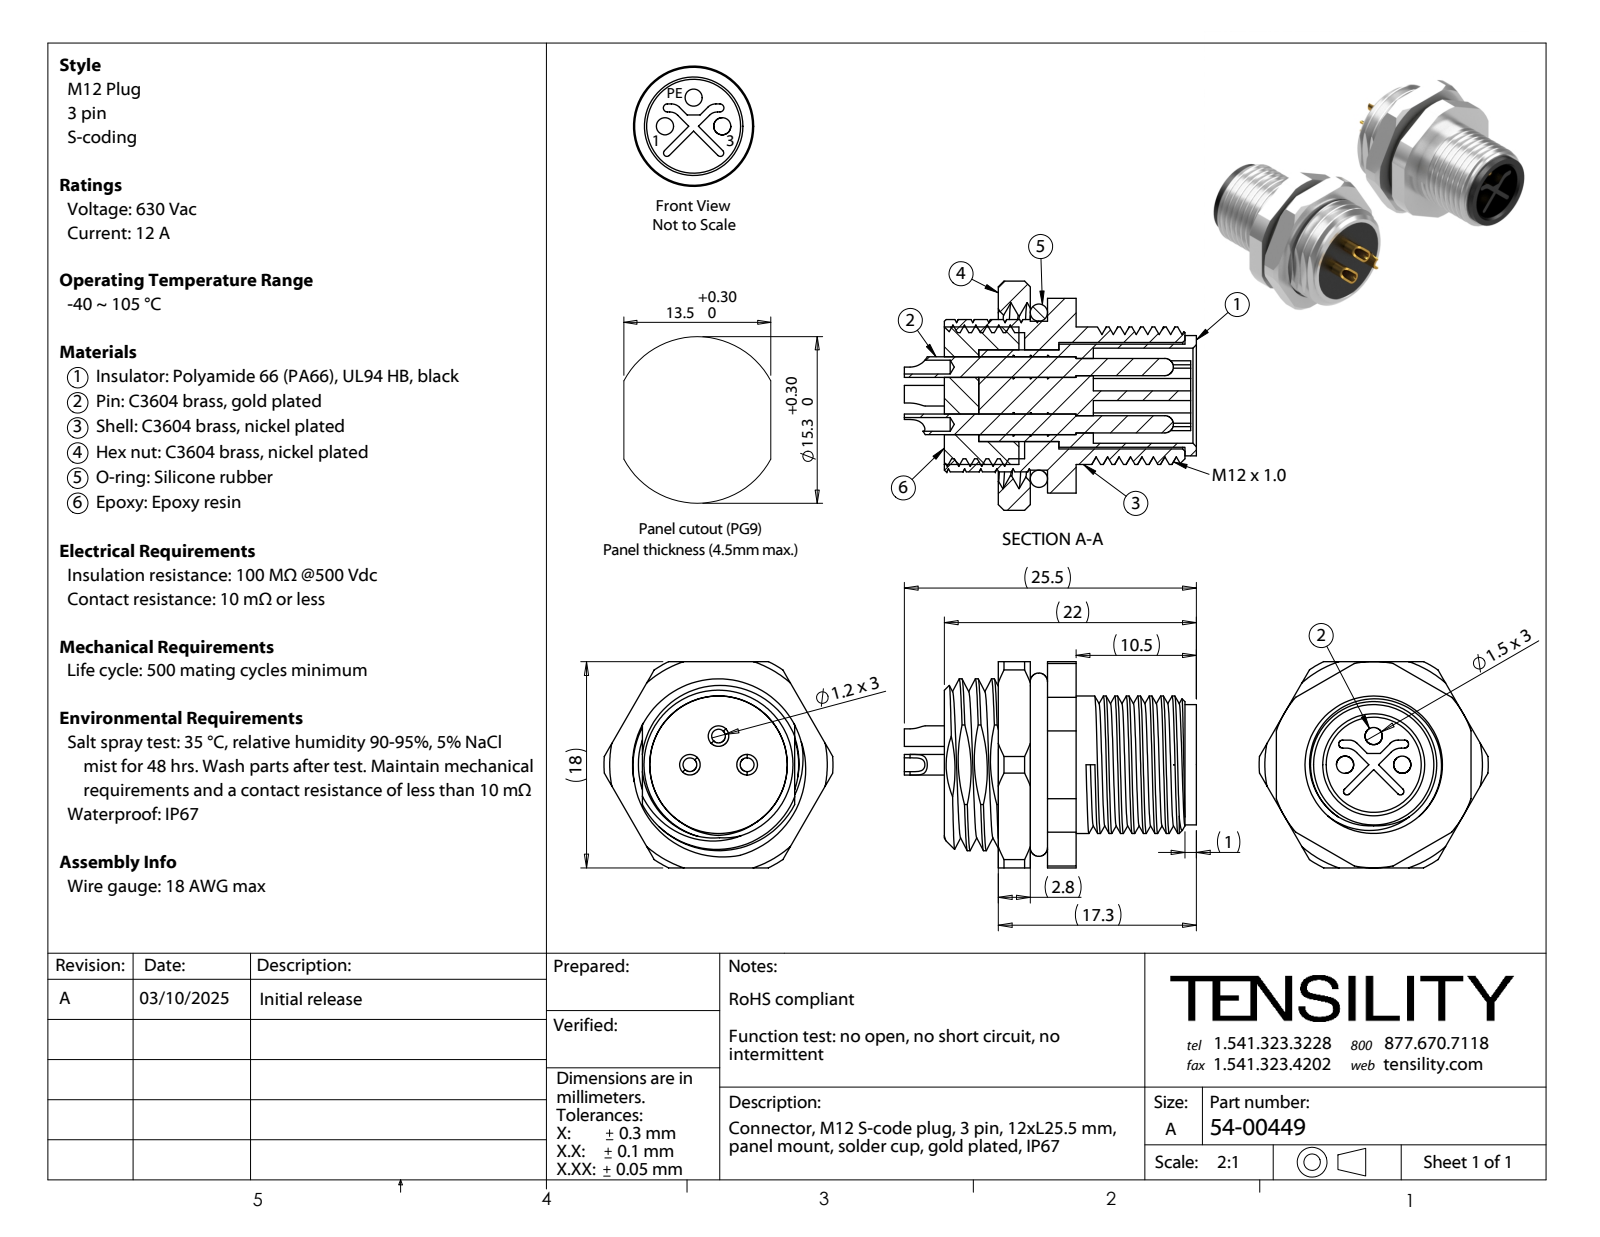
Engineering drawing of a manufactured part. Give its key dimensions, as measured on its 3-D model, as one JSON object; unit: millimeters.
{"part_name": "54-00449-03; 54-00449-02; 54-00449; 54-00449-03L (+3 more)", "step_written_by": "SolidWorks 2021 (CONFIG_CONTROL_DESIGN)", "units": "millimeters", "bodies": {"solids": 8, "faces": 309, "planar": 83, "cylindrical": 144, "other": 82}, "overall_size": [25.5, 20, 18], "volume_mm3": 3000, "surface_area_mm2": 5707, "round_holes": [[1.2, 3], [1.5, 3], [8, 1], [8.3, 1], [9.3, 1], [11, 1], [14, 1]], "round_bosses_or_shafts": [[1.8, 3], [13, 1], [12, 1], [10.5, 1], [9, 1]], "partial_cylinders_radius": [[0.3, 2], [0.35, 2], [1, 2], [1.28, 2], [1.7, 2], [7.5, 1], [9, 1], [10, 1]], "face_to_face_distances": [2.5, 4, 1.5, 3, 11.5, 4.5, 9, 6, 1, 18], "hole_center_spacings": [2.5, 3.54, 5]}
